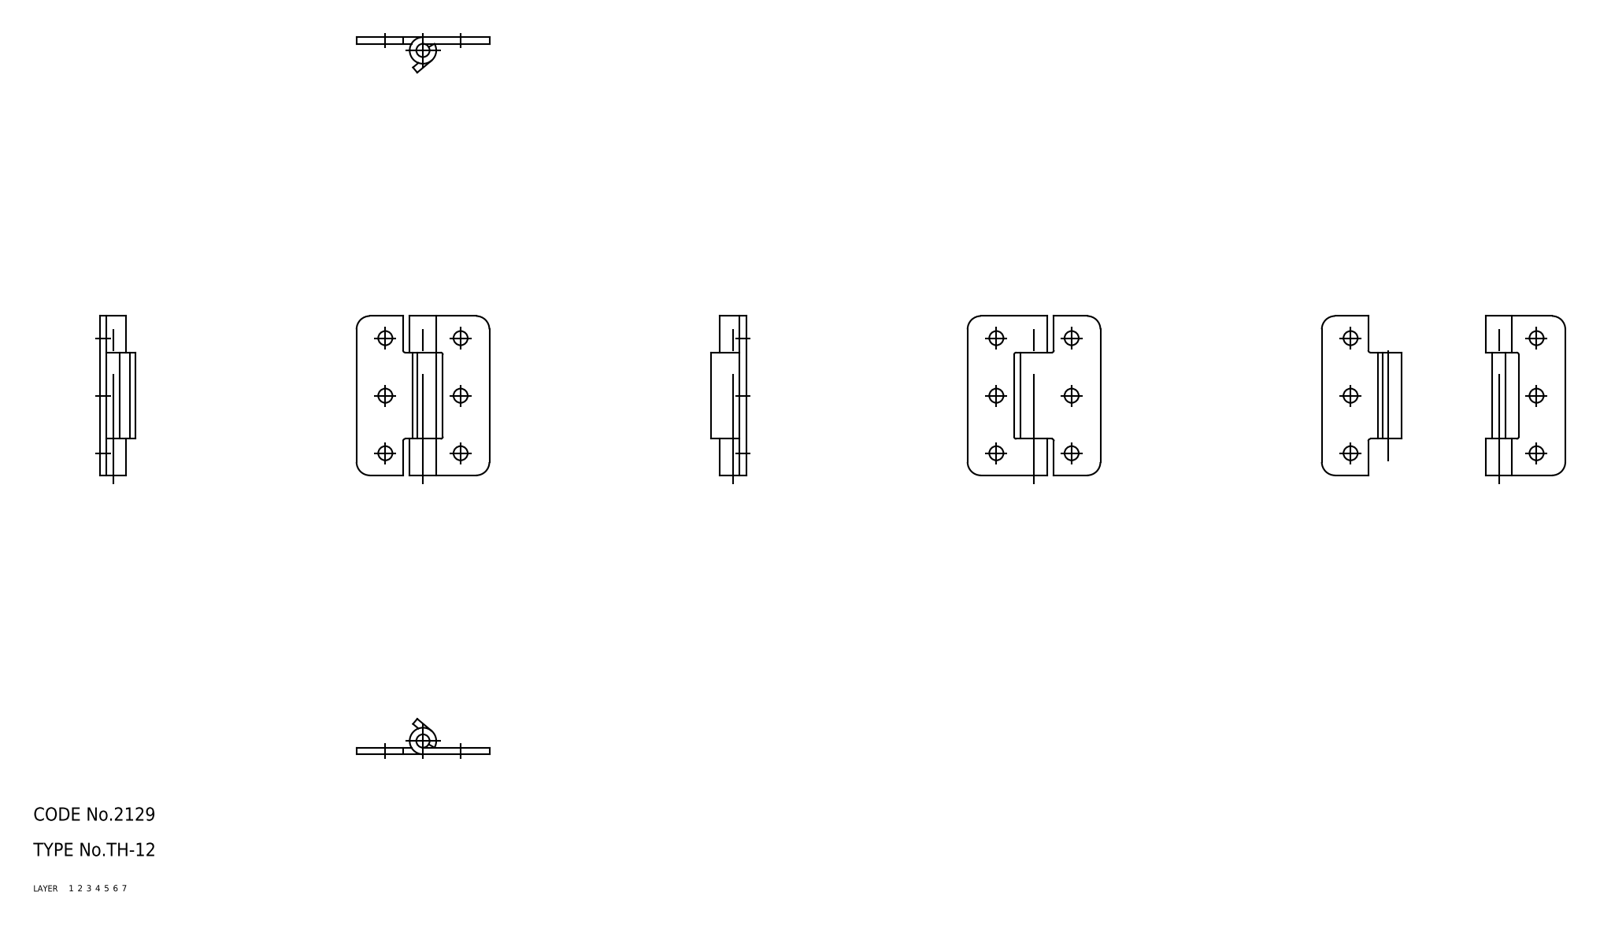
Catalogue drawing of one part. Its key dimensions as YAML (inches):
part_name: "shaft; hinge piece_B; hinge piece_A; TH_12_294_36"
step_written_by: "CADfix (AUTOMOTIVE_DESIGN)"
units: inches
bodies: {solids: 3, faces: 52, planar: 0, cylindrical: 0, other: 52}
overall_size: [1.417, 1.181, 0.315]
volume: 0.129
surface_area: 5.185
